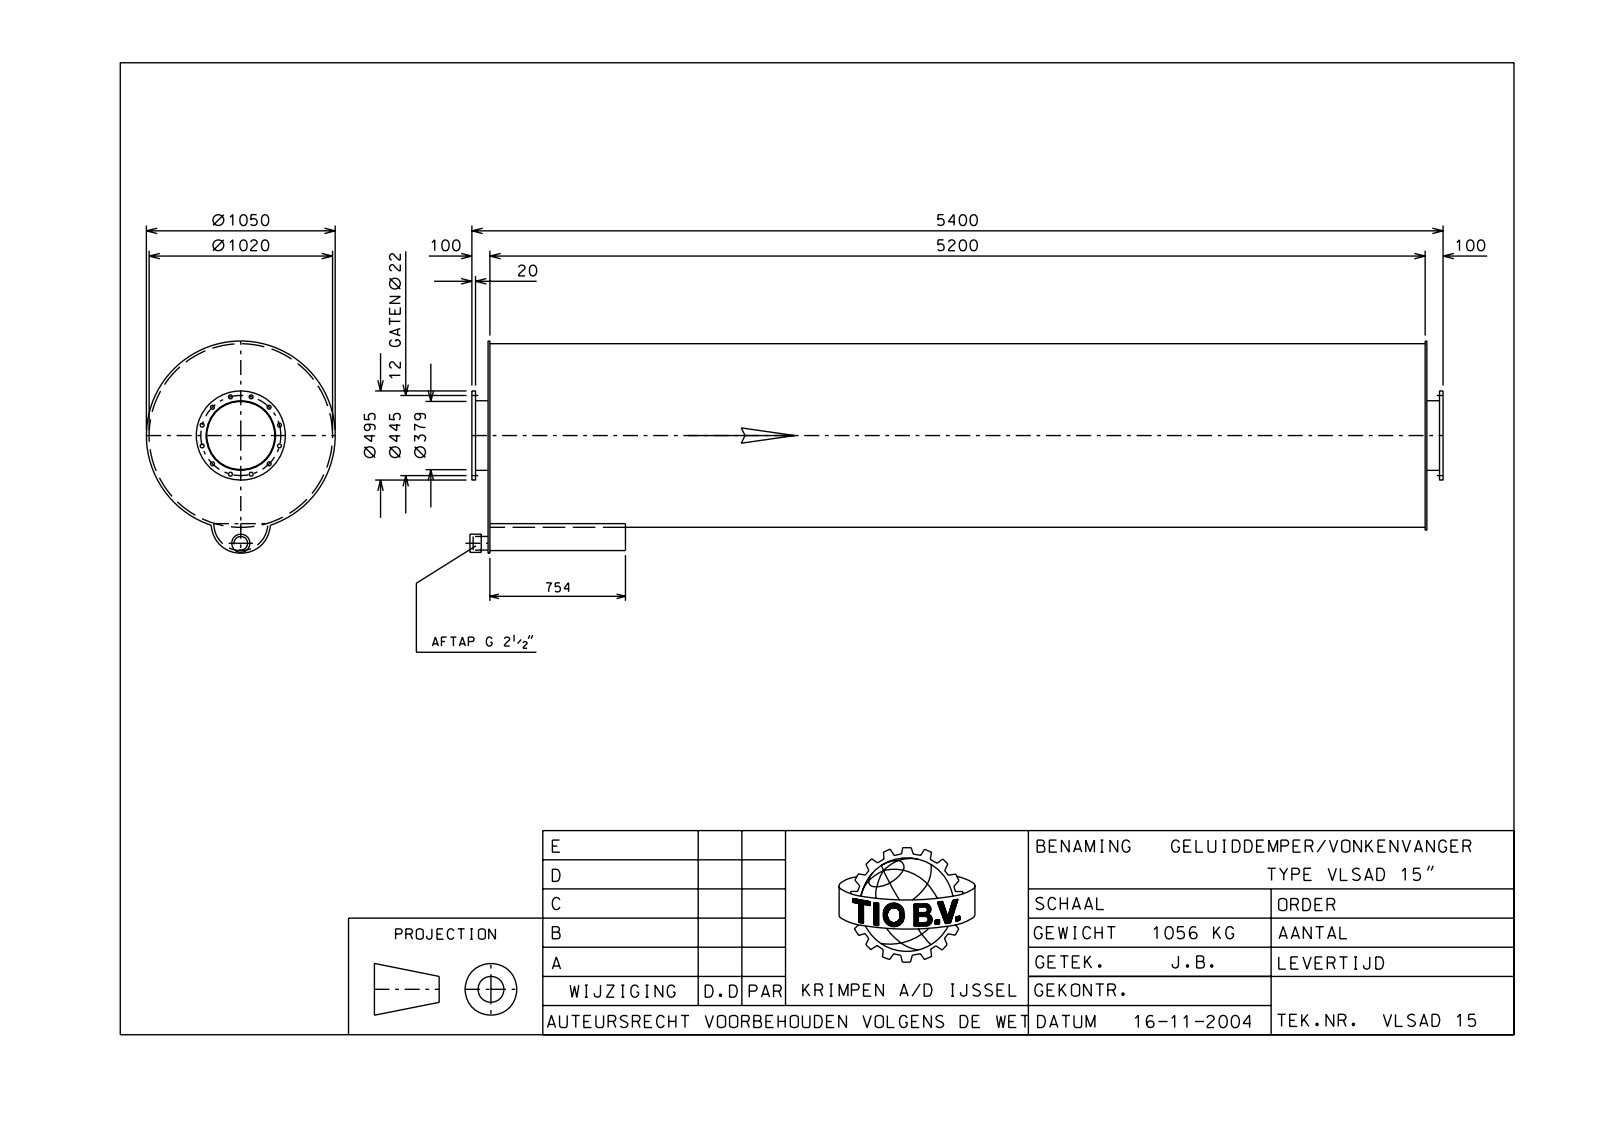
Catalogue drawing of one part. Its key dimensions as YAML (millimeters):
part_name: "MAAT3D"
step_written_by: "Autodesk Inventor 2015 (AUTOMOTIVE_DESIGN)"
units: millimeters
bodies: {solids: 13, faces: 86, planar: 36, cylindrical: 50, other: 0}
overall_size: [5400, 1178.6, 1050]
volume: 87320000
surface_area: 38230000
round_holes:
  - {diameter: 22, count: 12}
  - {diameter: 69.3, count: 1}
  - {diameter: 379, count: 1}
  - {diameter: 389, count: 1}
  - {diameter: 1012, count: 1}
round_bosses_or_shafts:
  - {diameter: 1050, count: 1}
  - {diameter: 1020, count: 1}
  - {diameter: 495, count: 1}
  - {diameter: 387, count: 1}
  - {diameter: 76.1, count: 1}
partial_cylinders:
  - {radius: 146, count: 1}
  - {radius: 150, count: 1}
  - {radius: 165, count: 1}
face_to_face_distances: [10, 5210, 5200, 5220, 90, 100, 5300, 5310, 5380, 70]
hole_center_spacings: [222.5, 429.84, 115.17, 314.67, 385.38, 445, 115.18, 314.66]
